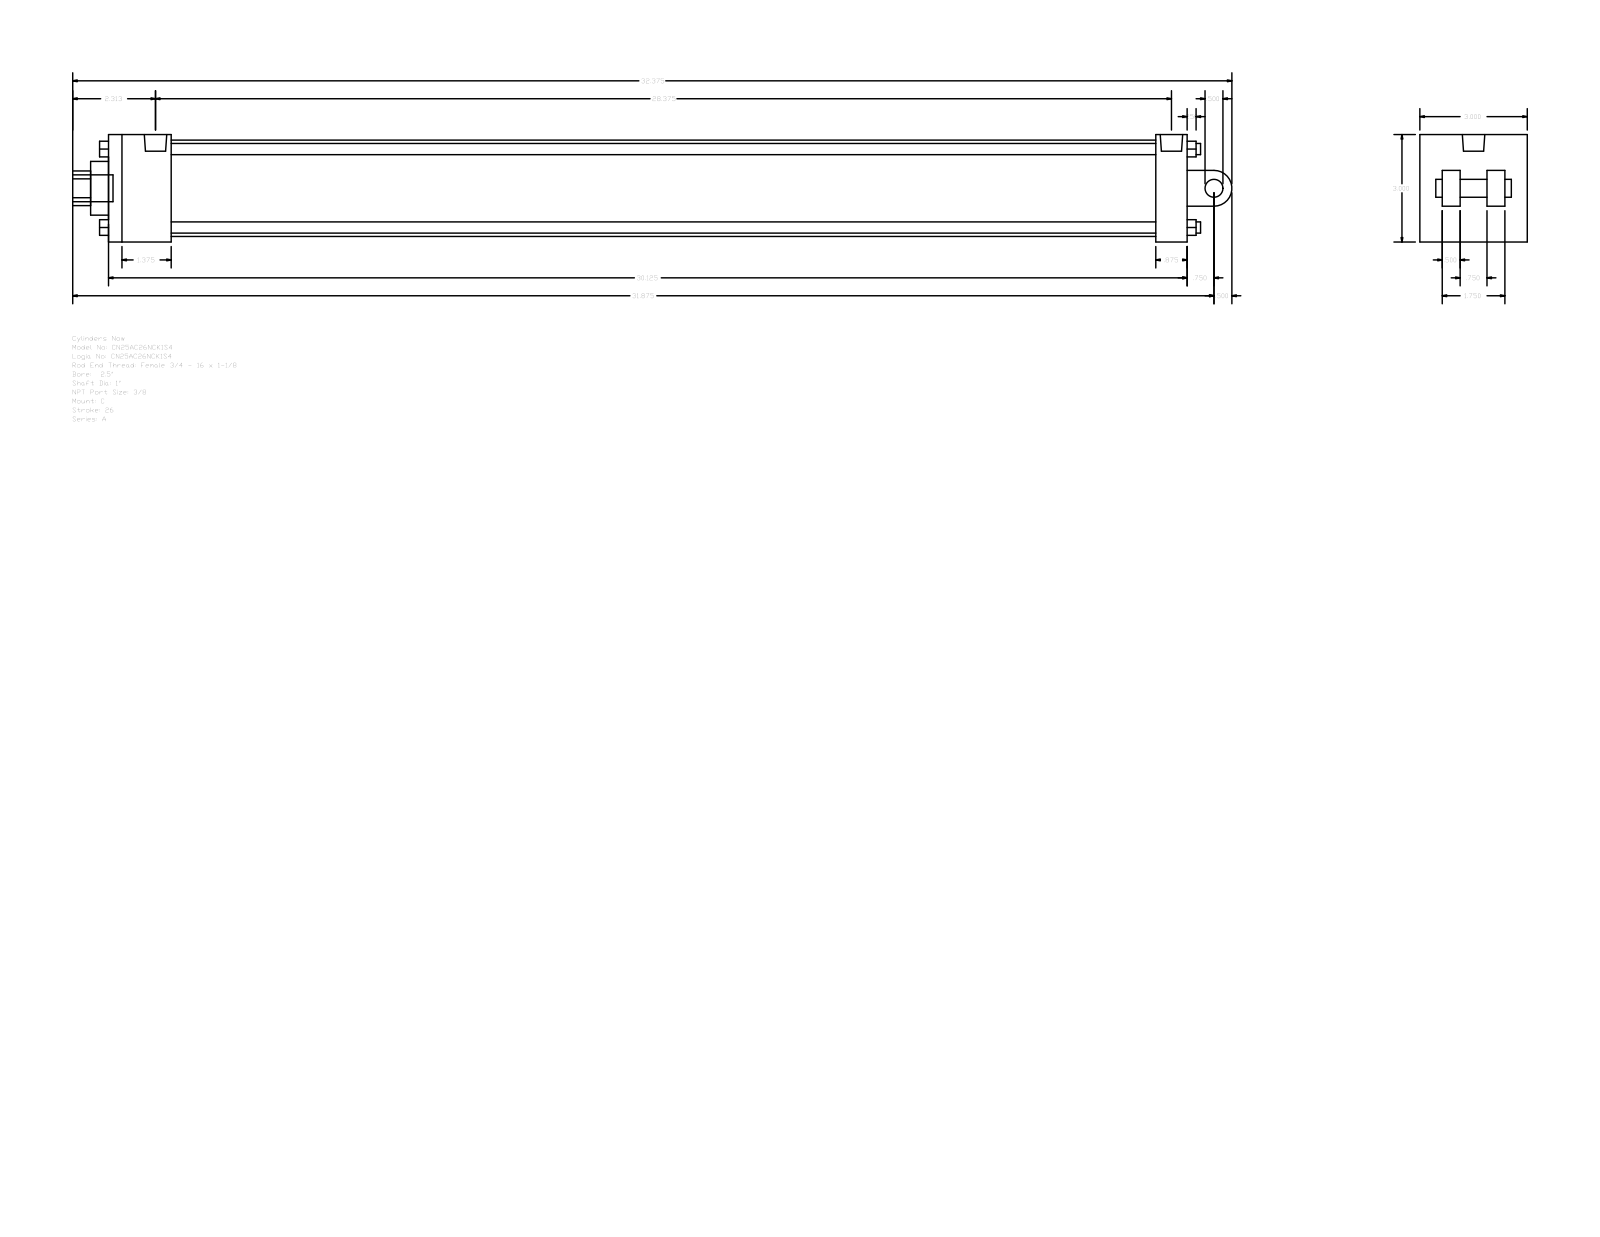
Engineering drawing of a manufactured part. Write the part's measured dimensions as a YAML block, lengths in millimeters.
part_name: "A_C__0250_1"
step_written_by: "GSSL Pune (CONFIG_CONTROL_DESIGN)"
units: millimeters
bodies: {solids: 0, faces: 135, planar: 102, cylindrical: 33, other: 0}
overall_size: [822.33, 76.2, 76.2]
round_holes:
  - {diameter: 5.56, count: 2}
  - {diameter: 15.93, count: 1}
  - {diameter: 25.4, count: 1}
  - {diameter: 38.1, count: 1}
  - {diameter: 68.33, count: 1}
round_bosses_or_shafts:
  - {diameter: 7.94, count: 4}
  - {diameter: 5.56, count: 2}
  - {diameter: 19.05, count: 1}
  - {diameter: 15.93, count: 1}
  - {diameter: 12.7, count: 1}
partial_cylinders:
  - {radius: 12.29, count: 1}
  - {radius: 12.7, count: 1}
face_to_face_distances: [76.2, 765.18, 12.7, 44.45, 742.95, 698.5, 720.73, 22.23, 15.87, 25.4]
hole_center_spacings: [2.38]
